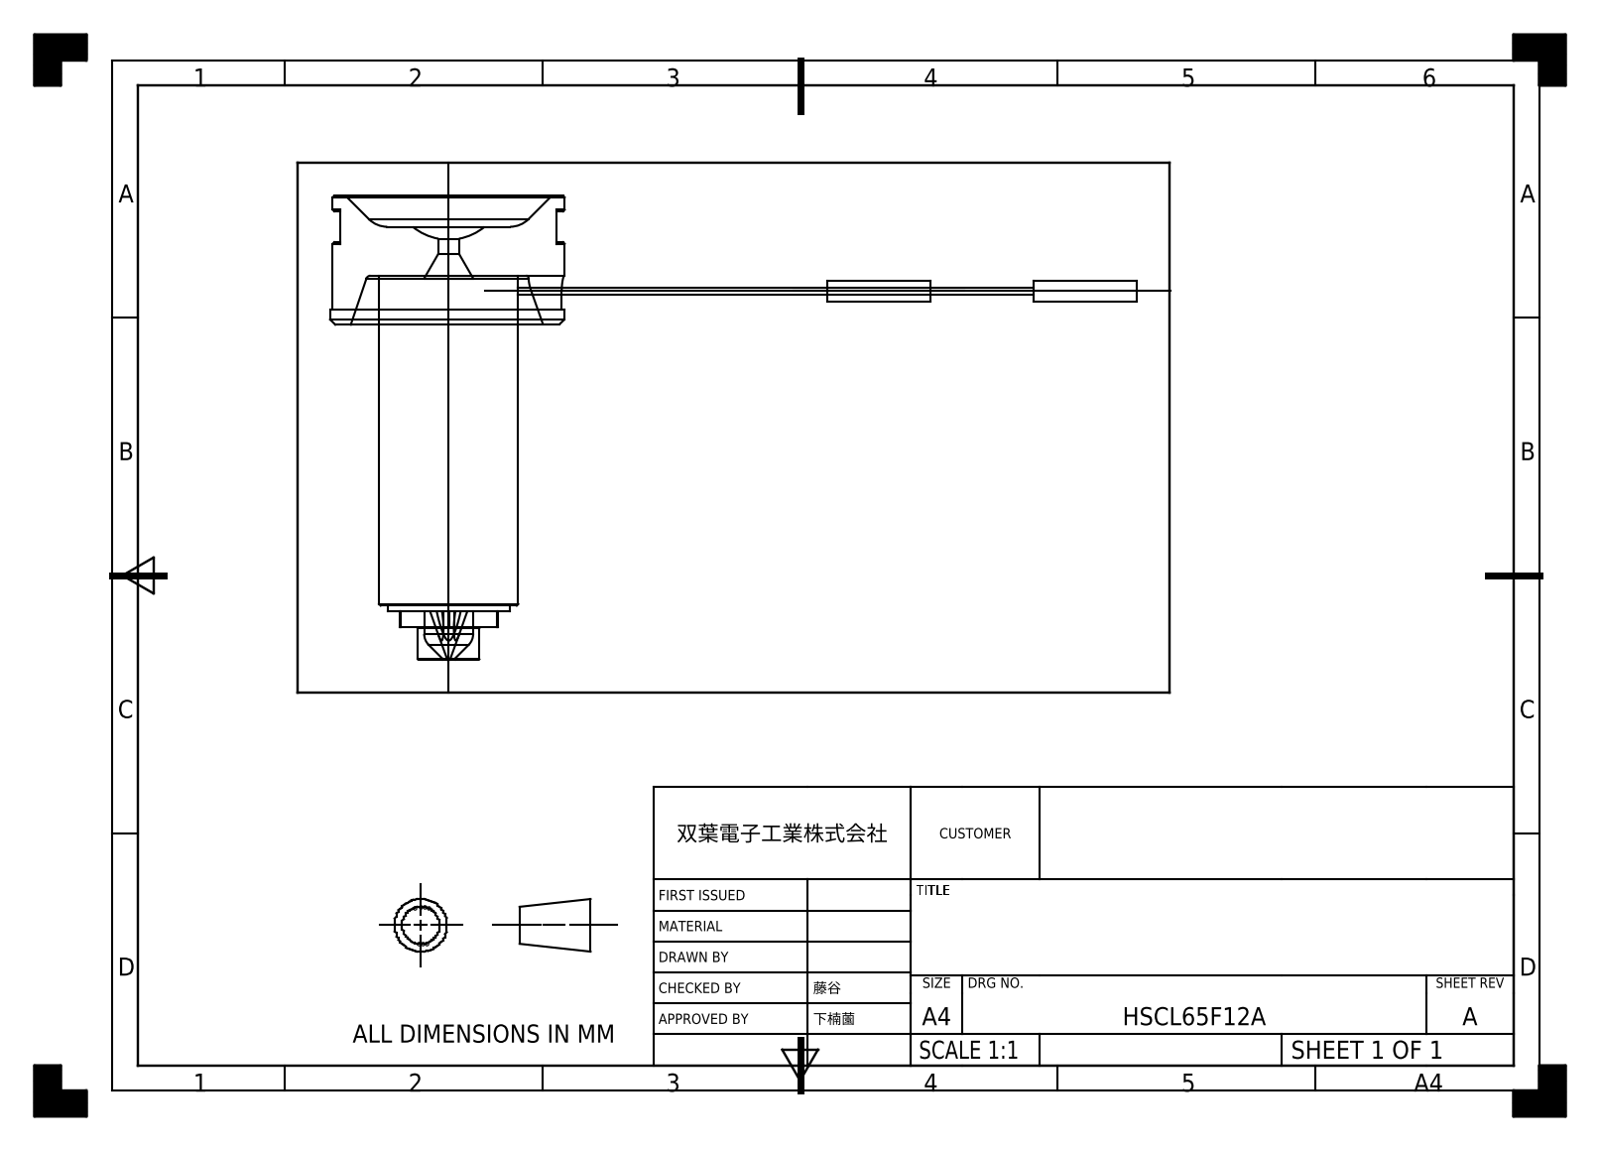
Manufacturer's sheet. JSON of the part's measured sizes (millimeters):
{"part_name": "HSCL65F12A", "step_written_by": "SIEMENS PLM Software NX 2023 (AUTOMOTIVE_DESIGN)", "units": "millimeters", "bodies": {"solids": 5, "faces": 75, "planar": 34, "cylindrical": 23, "other": 18}, "overall_size": [156.5, 90, 46], "volume_mm3": 63378, "surface_area_mm2": 15454, "round_holes": [[2.5, 1], [4, 1], [9.5, 1]], "round_bosses_or_shafts": [[4, 2], [1.2, 2], [46, 1], [45, 1], [27, 1], [23.8, 1], [12, 1]], "partial_cylinders_radius": [[2.8, 3], [3, 2], [10.9, 1]], "face_to_face_distances": [9.5, 19, 6, 25, 74.5, 65, 83.7, 77.7, 58.7, 15.5]}
